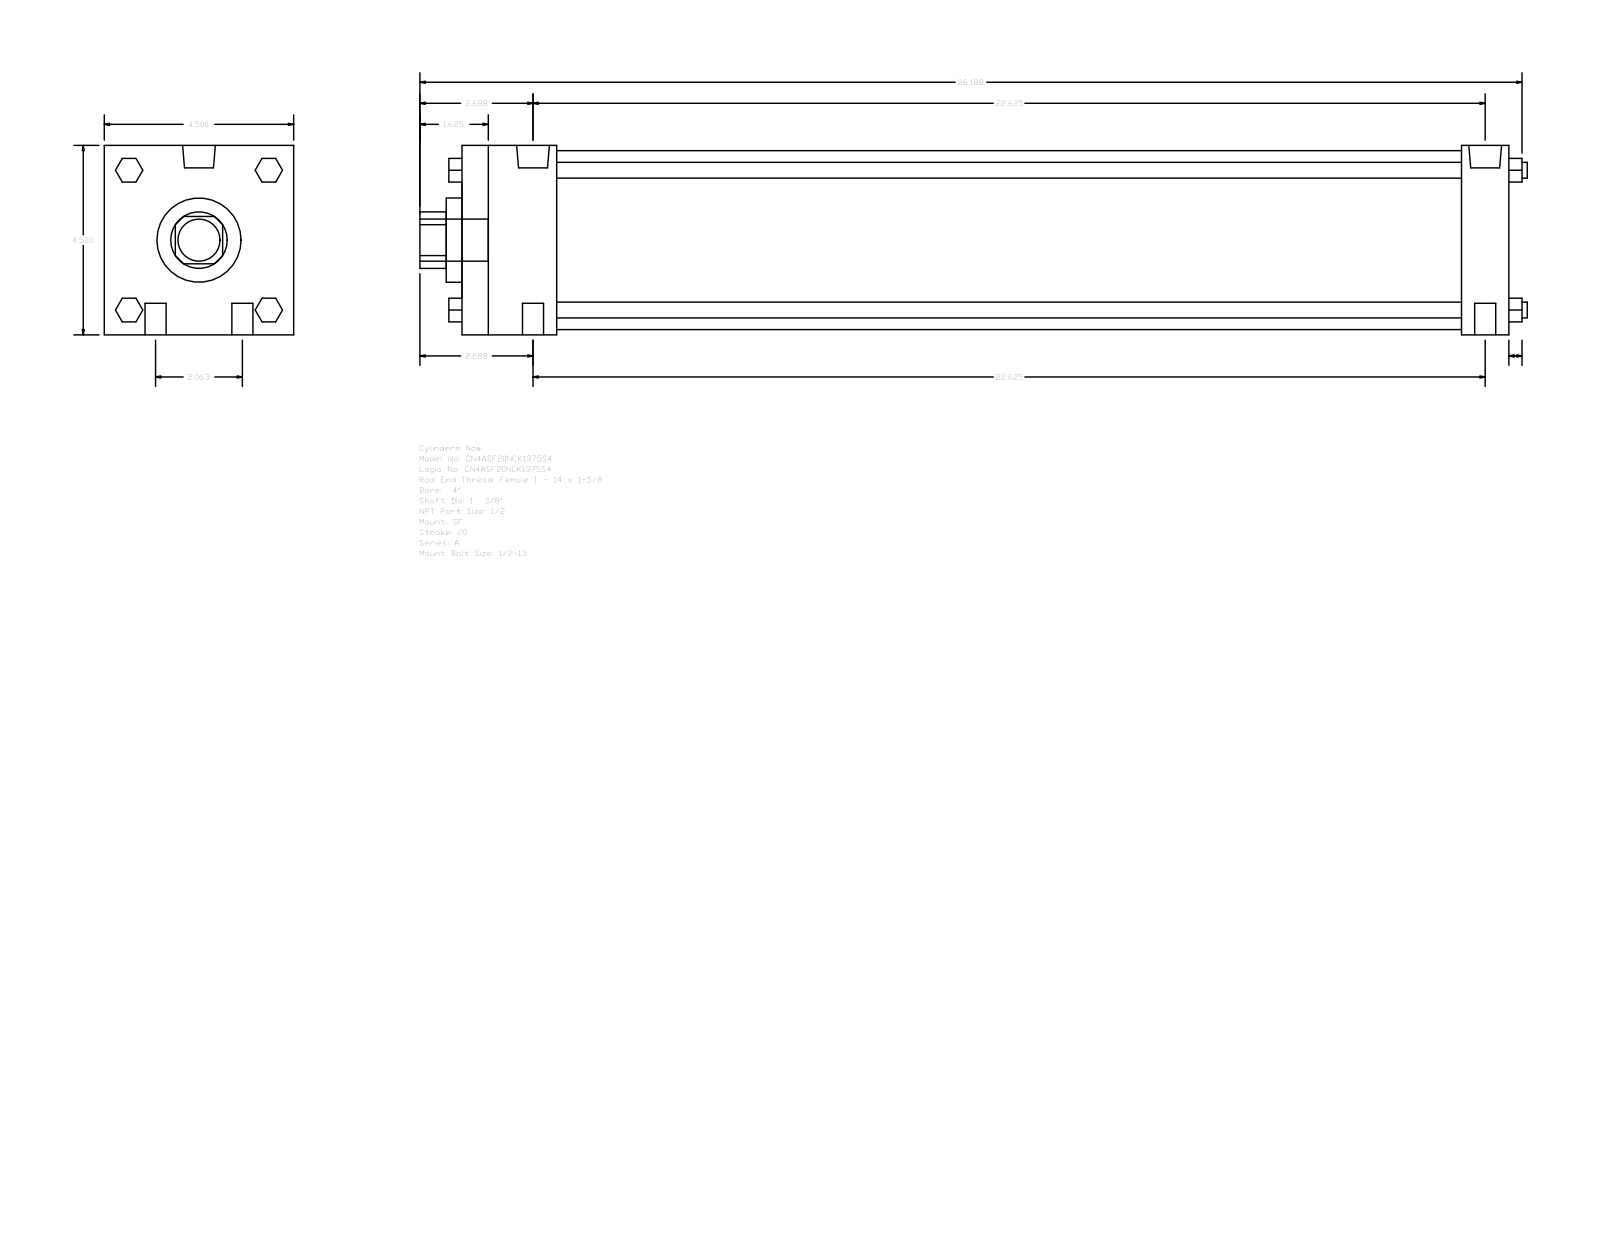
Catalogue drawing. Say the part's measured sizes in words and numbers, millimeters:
The part is named "A_SF__0400_1.375". Its 3-D file was written by "GSSL Pune (CONFIG_CONTROL_DESIGN)". It is 0 solids with 124 faces: 94 planar, 30 cylindrical and 0 other. Overall it measures 668.34 by 114.3 by 114.3 millimeters. Round holes: 1 of diameter 34.92, 1 of diameter 50.8, 1 of diameter 107.95. Round bosses or shafts: 4 of diameter 12.7, 4 of diameter 9.53, 2 of diameter 19.77, 2 of diameter 8.73, 1 of diameter 25.4. Partial cylindrical surfaces (rounded edges, fillets, slot ends): 1 of radius 17.06. The main face-to-face distances are 114.3, 631.83, 28.58, 603.25, 57.15, 546.1, 574.68, 14.29, 9.52, 66.67.
